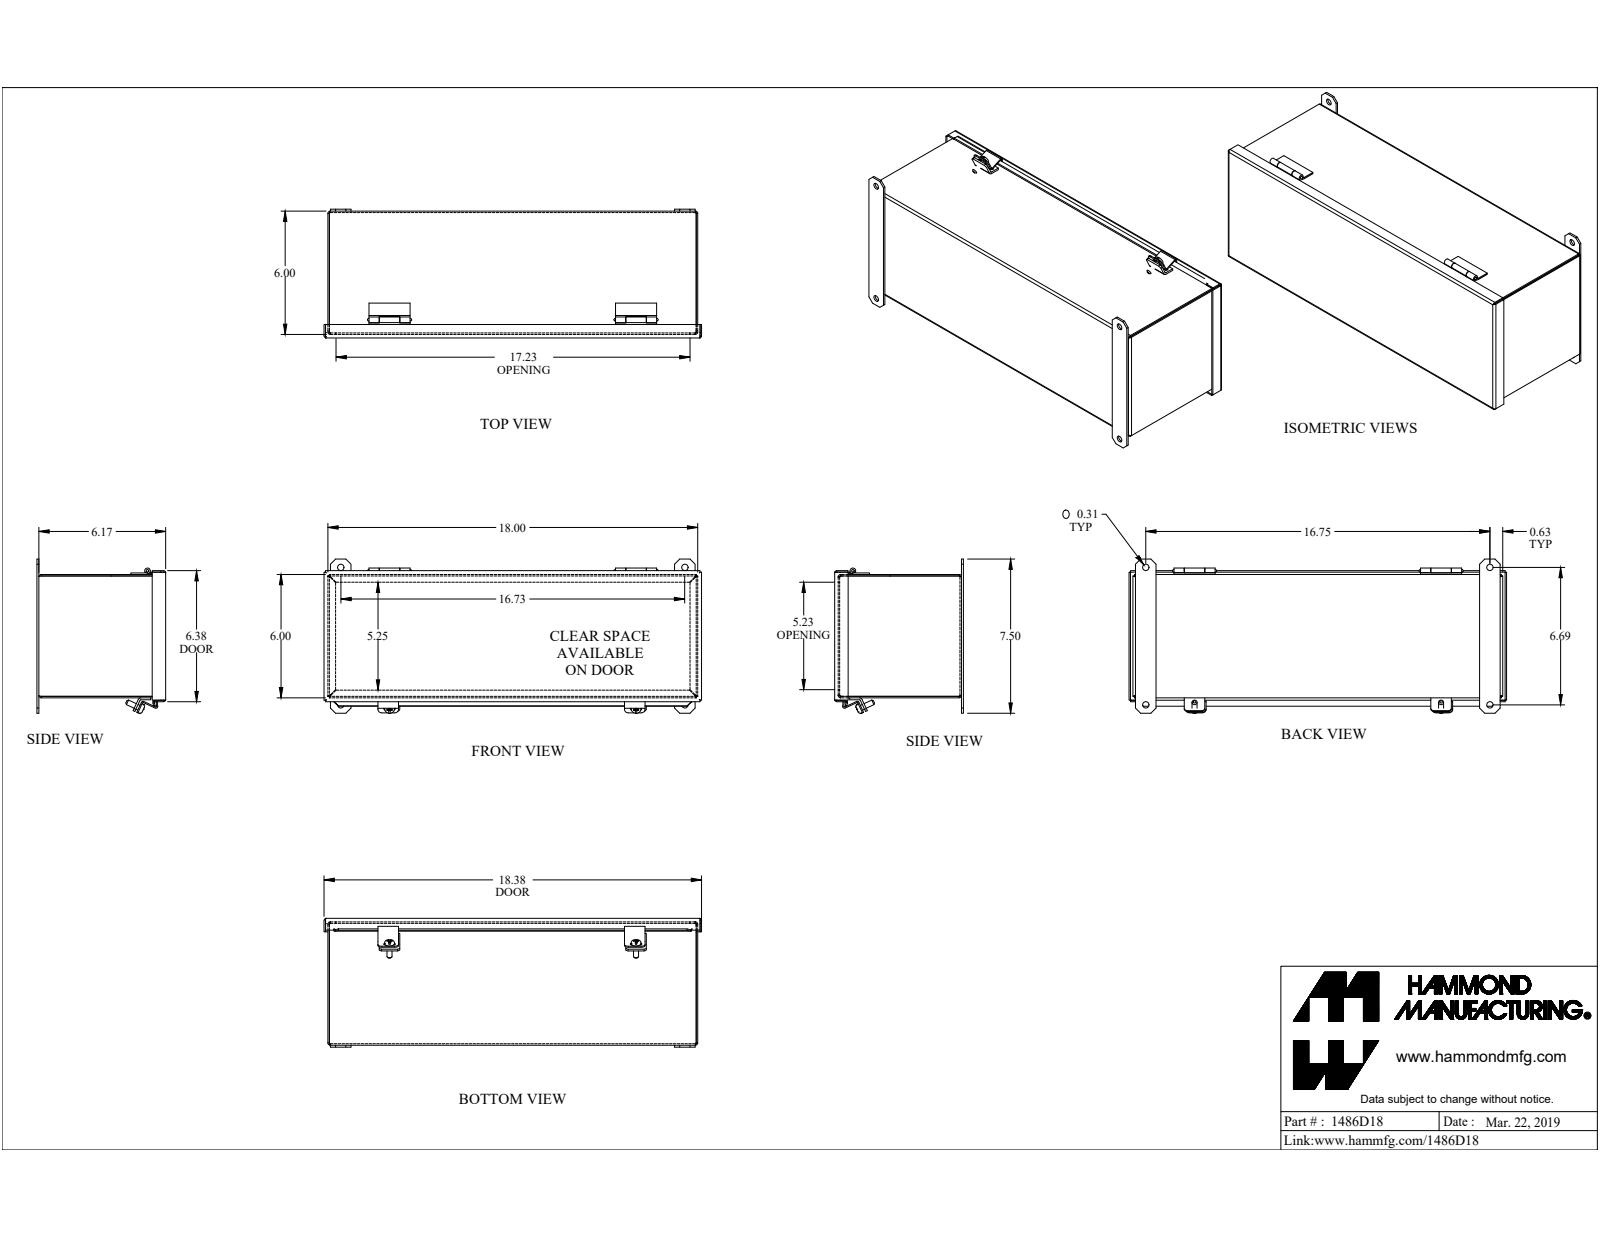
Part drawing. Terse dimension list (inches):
name: 1486D18
written by: SolidWorks 2019 (CONFIG_CONTROL_DESIGN)
unit: in
bodies: 20 solids, 420 faces (278 planar, 98 cylindrical, 44 other)
size: 18.375 × 7.506 × 6.267
volume: 48.35 in³; area: 1 258 in²
holes: 4× ⌀0.313, 2× ⌀0.213, 1× ⌀0.125
bosses: 2× ⌀0.48, 2× ⌀0.246, 1× ⌀0.275, 1× ⌀0.125
rounds: 13× R0.036, 13× R0.108, 12× R0.25, 8× R0.188, 4× R0.01, 4× R0.141, 2× R0.029, 2× R0.086
face distances: 0.072, 5.928, 6.1, 6, 5.856, 6.172, 6.028, 17.928, 0.187, 0.259
hole spacings: 6.688, 16.75, 18.036, 12
